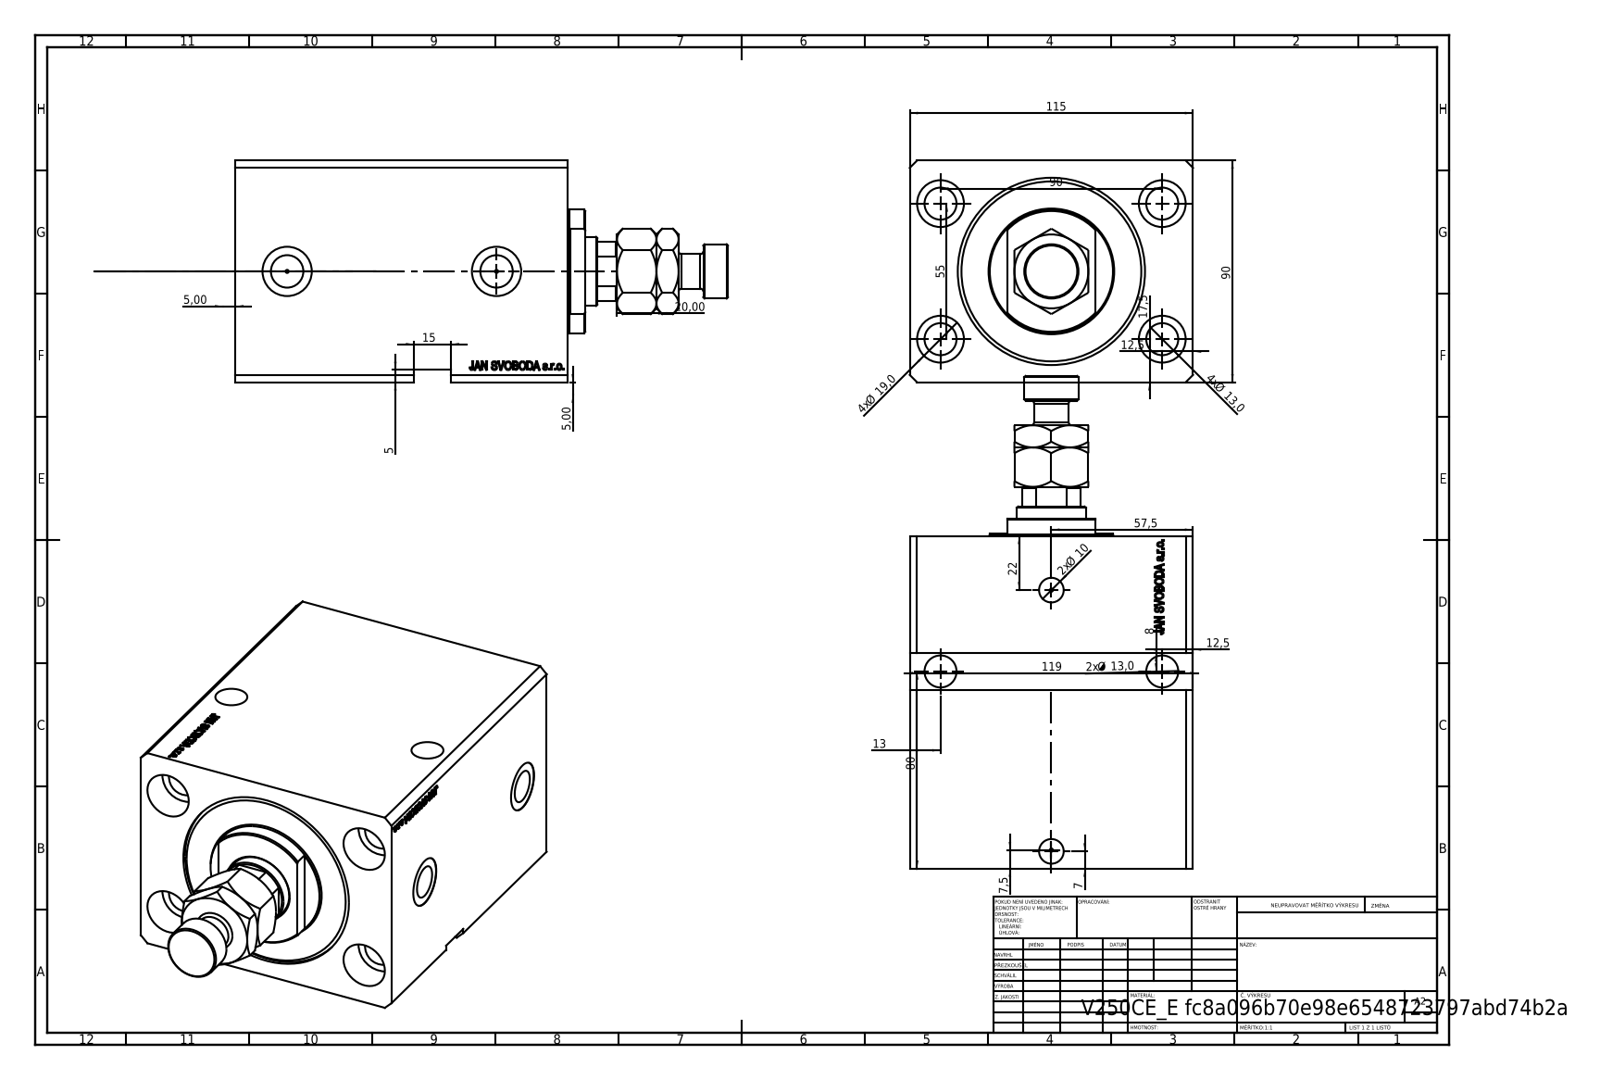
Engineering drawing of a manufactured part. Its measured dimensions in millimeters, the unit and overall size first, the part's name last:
Units: millimetres
Overall size (bounding box): 199.9 × 115 × 90
Round holes (diameter × count): ⌀13 ×6, ⌀1.25 ×4, ⌀19 ×4, ⌀10 ×2, ⌀13.16 ×2, ⌀20 ×2, ⌀18.5 ×1, ⌀28 ×1, ⌀63 ×1, ⌀76 ×1
Round bosses / shafts (diameter × count): ⌀50 ×1, ⌀22 ×1, ⌀14 ×1
Partial cylindrical surfaces — rounded edges, fillets, slot ends (radius × count): R13.5 ×1
Main face-to-face distances: 90, 115, 135, 17.9, 117.1, 87, 104.9, 30.1, 50, 54.9
Hole centre spacings: 52.74, 90, 55, 55.8, 85.3, 85.76, 105.48, 0.53
Volume: 1 183 000 mm³ · Surface area: 179 057 mm²
Bodies: 4 solids, 1005 faces (487 planar, 100 cylindrical, 418 other)
Part name (STEP PRODUCT): V250CE_E_Body; V250CE_VC_E; V250CE_C_VCP; MFA
STEP written by: SolidWorks 2019 (CONFIG_CONTROL_DESIGN)
